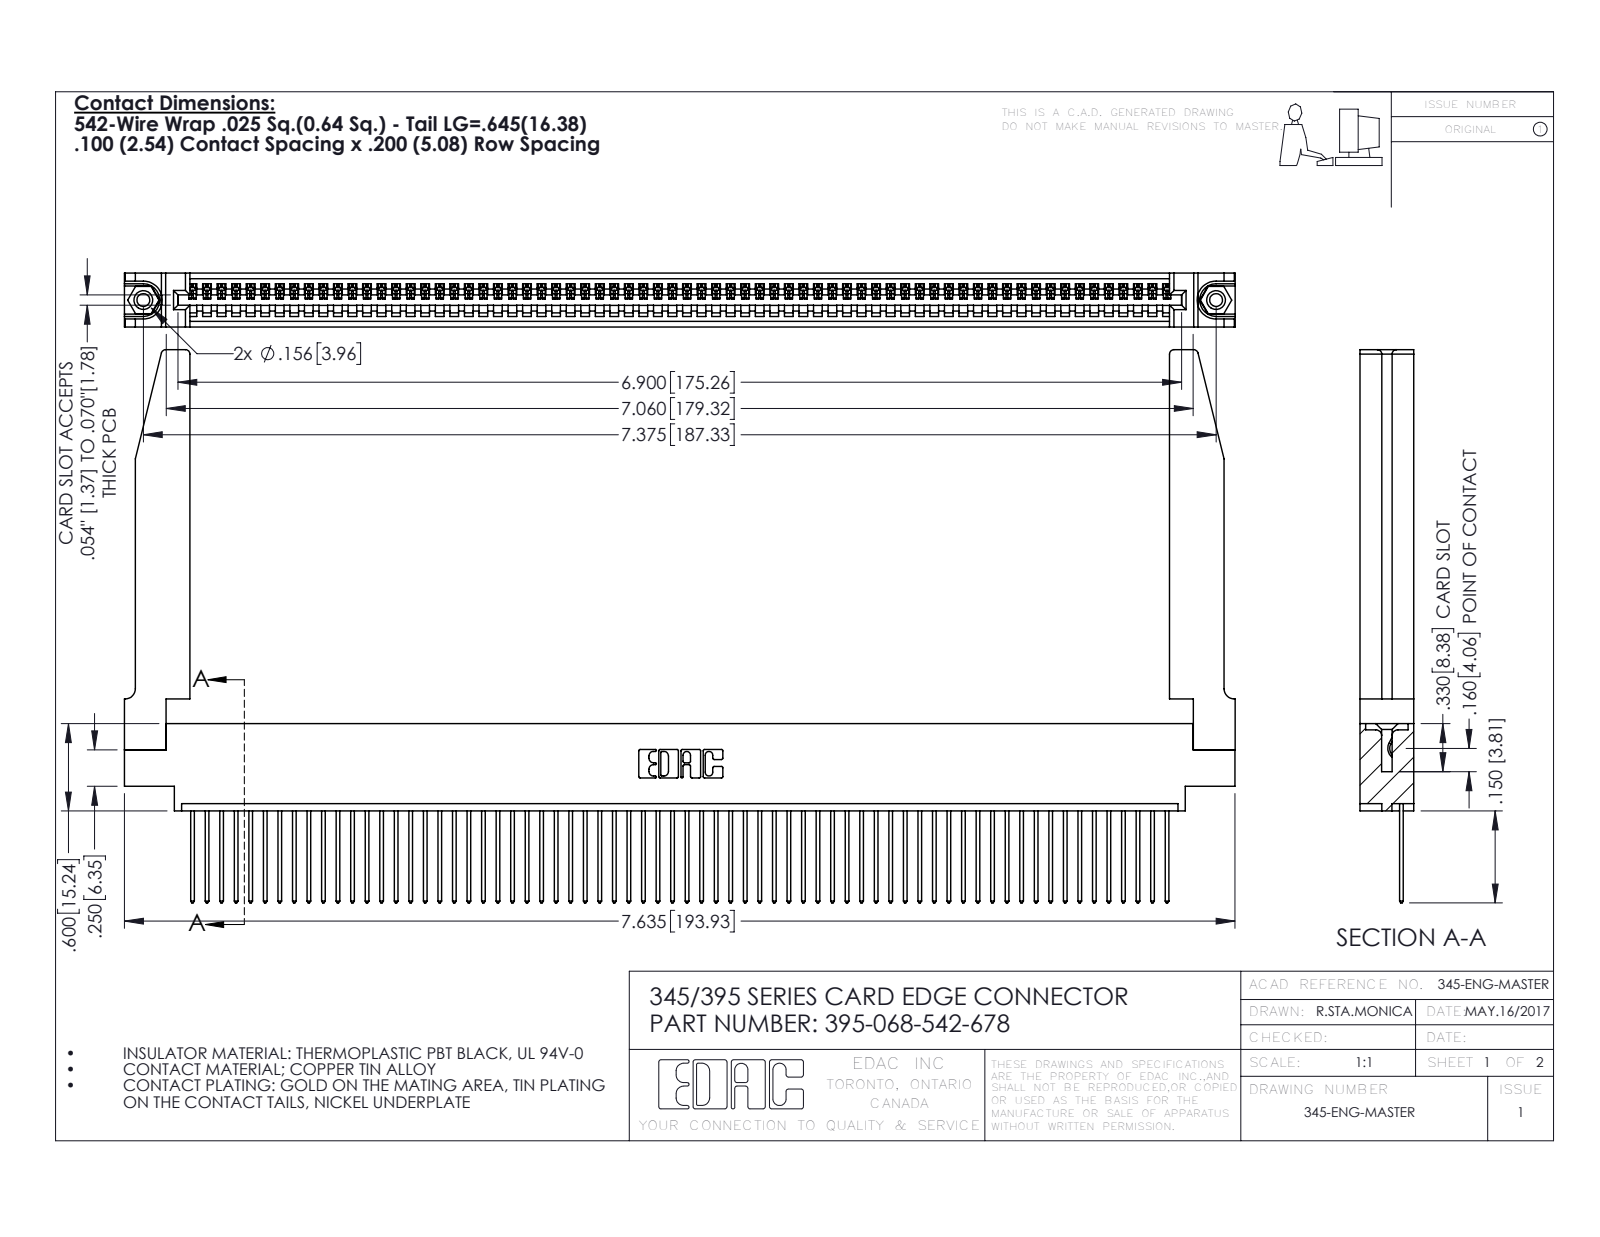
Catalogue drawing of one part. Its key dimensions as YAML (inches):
part_name: "345-250-001_345-250-001-102; 345-292-001_345-293-142; 395-068-542-678; 345 Part_0.170 Offset - 0.156 Dia-TH (+1 more)"
step_written_by: "SolidWorks 2016 (CONFIG_CONTROL_DESIGN)"
units: inches
bodies: {solids: 73, faces: 4308, planar: 2946, cylindrical: 1310, other: 52}
overall_size: [7.636, 3.802, 0.37]
volume: 1.614
surface_area: 51.3
round_holes:
  - {diameter: 0.089, count: 2}
  - {diameter: 0.125, count: 2}
  - {diameter: 0.156, count: 2}
  - {diameter: 0.064, count: 1}
round_bosses_or_shafts:
  - {diameter: 0.155, count: 2}
partial_cylinders:
  - {radius: 0.006, count: 136}
  - {radius: 0.01, count: 136}
  - {radius: 0.01, count: 22}
  - {radius: 0.03, count: 8}
  - {radius: 0.007, count: 6}
  - {radius: 0.031, count: 6}
  - {radius: 0.026, count: 3}
  - {radius: 0.031, count: 2}
face_to_face_distances: [0.072, 0.298, 0.37, 0.098, 0.272, 0.025, 0.2, 0.225, 0.175, 0.149]
hole_center_spacings: [0.27, 7.139, 7.375]
